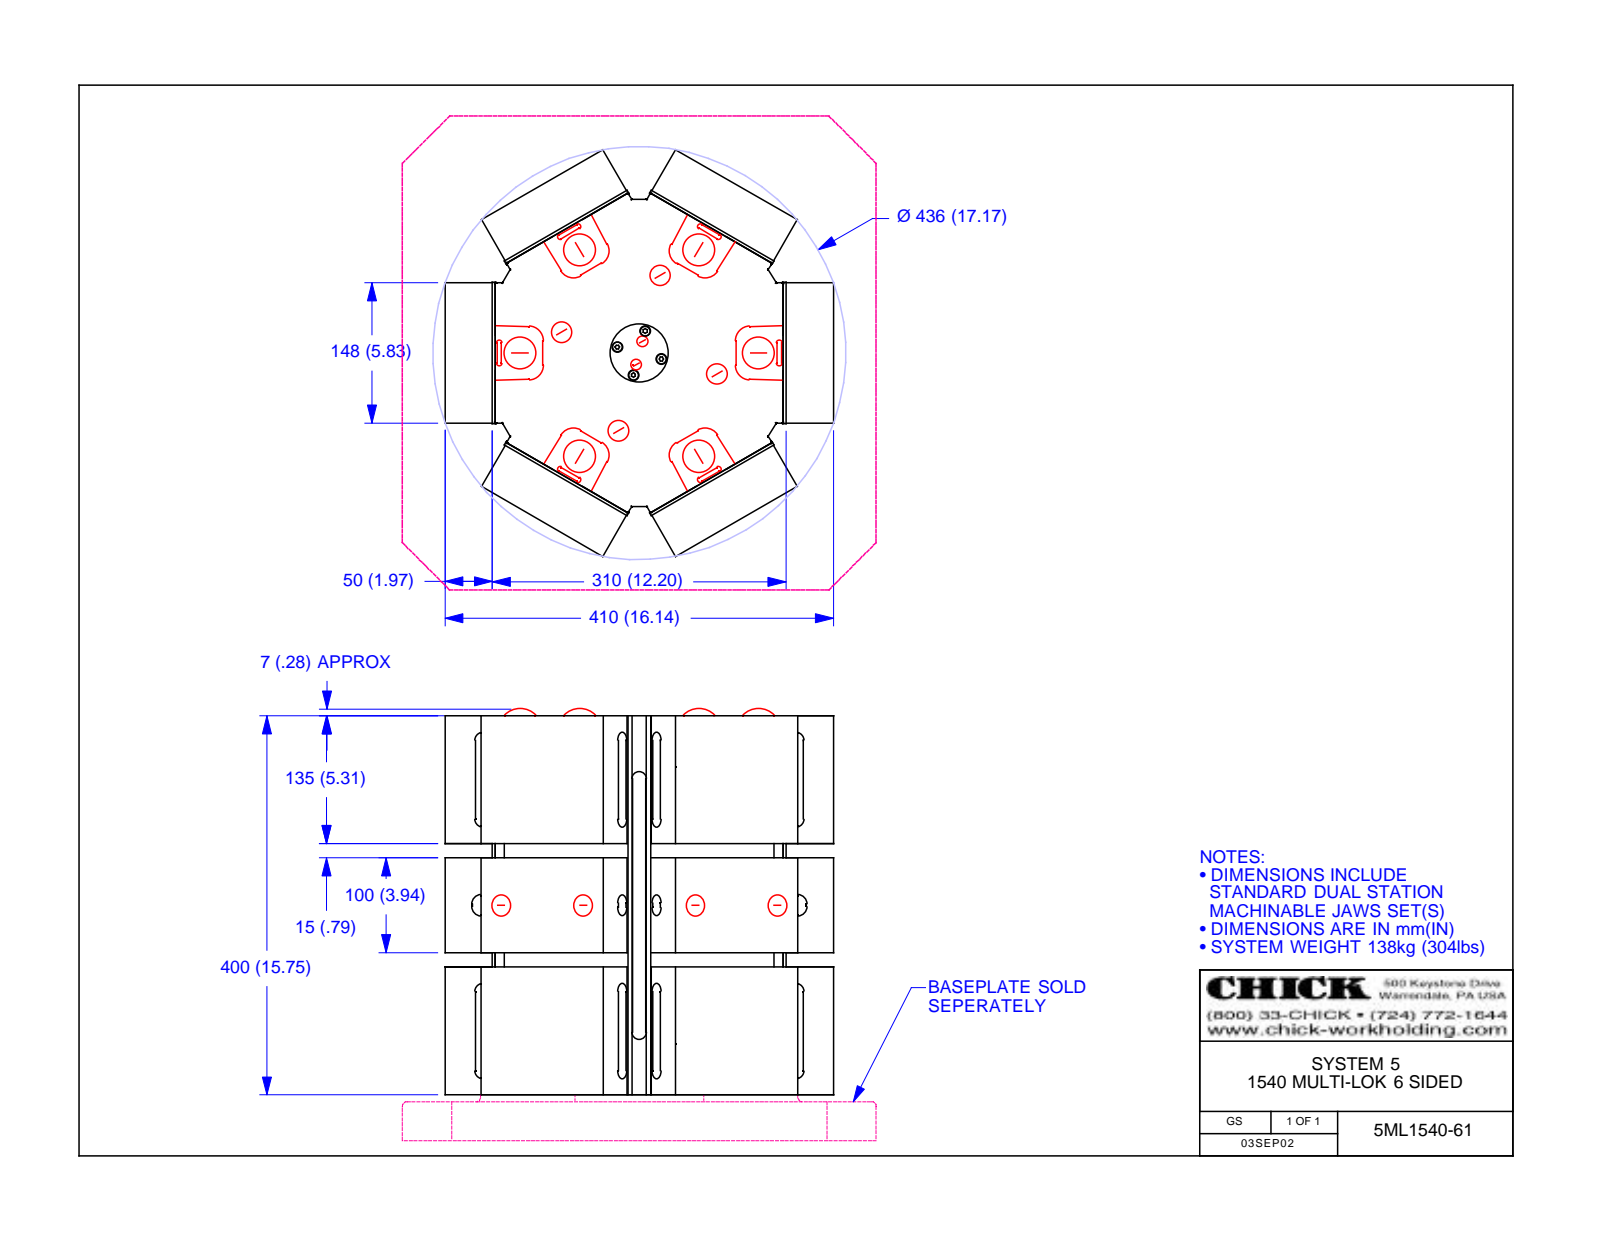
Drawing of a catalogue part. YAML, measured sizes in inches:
part_name: "5ML1540-61; 5CLM1540-61; 5CP1540-ST; 5DS1540-15-50 (+2 more)"
step_written_by: "Autodesk Inventor 2013 (AUTOMOTIVE_DESIGN)"
units: inches
bodies: {solids: 25, faces: 3757, planar: 1889, cylindrical: 678, other: 1190}
overall_size: [16.835, 16.142, 16.031]
volume: 2639
surface_area: 4459
round_holes:
  - {diameter: 0.407, count: 30}
  - {diameter: 0.433, count: 30}
  - {diameter: 0.715, count: 30}
  - {diameter: 1.062, count: 30}
  - {diameter: 0.669, count: 20}
  - {diameter: 0.413, count: 10}
  - {diameter: 0.709, count: 10}
  - {diameter: 0.787, count: 10}
  - {diameter: 0.394, count: 7}
  - {diameter: 0.398, count: 6}
  - {diameter: 0.16, count: 5}
  - {diameter: 0.27, count: 5}
round_bosses_or_shafts:
  - {diameter: 0.335, count: 12}
  - {diameter: 0.302, count: 5}
  - {diameter: 0.187, count: 5}
  - {diameter: 0.787, count: 4}
partial_cylinders:
  - {radius: 0.079, count: 156}
  - {radius: 0.118, count: 24}
  - {radius: 0.626, count: 24}
  - {radius: 0.016, count: 20}
  - {radius: 0.047, count: 20}
  - {radius: 0.065, count: 10}
  - {radius: 0.111, count: 10}
  - {radius: 0.276, count: 10}
face_to_face_distances: [0.118, 12.087, 1.969, 12.205, 2.087, 14.055, 14.173, 11.969, 2.244, 3.583]
hole_center_spacings: [4.921, 6.302, 3.937, 9.843, 10.601, 5.512, 3.937, 0.048]
